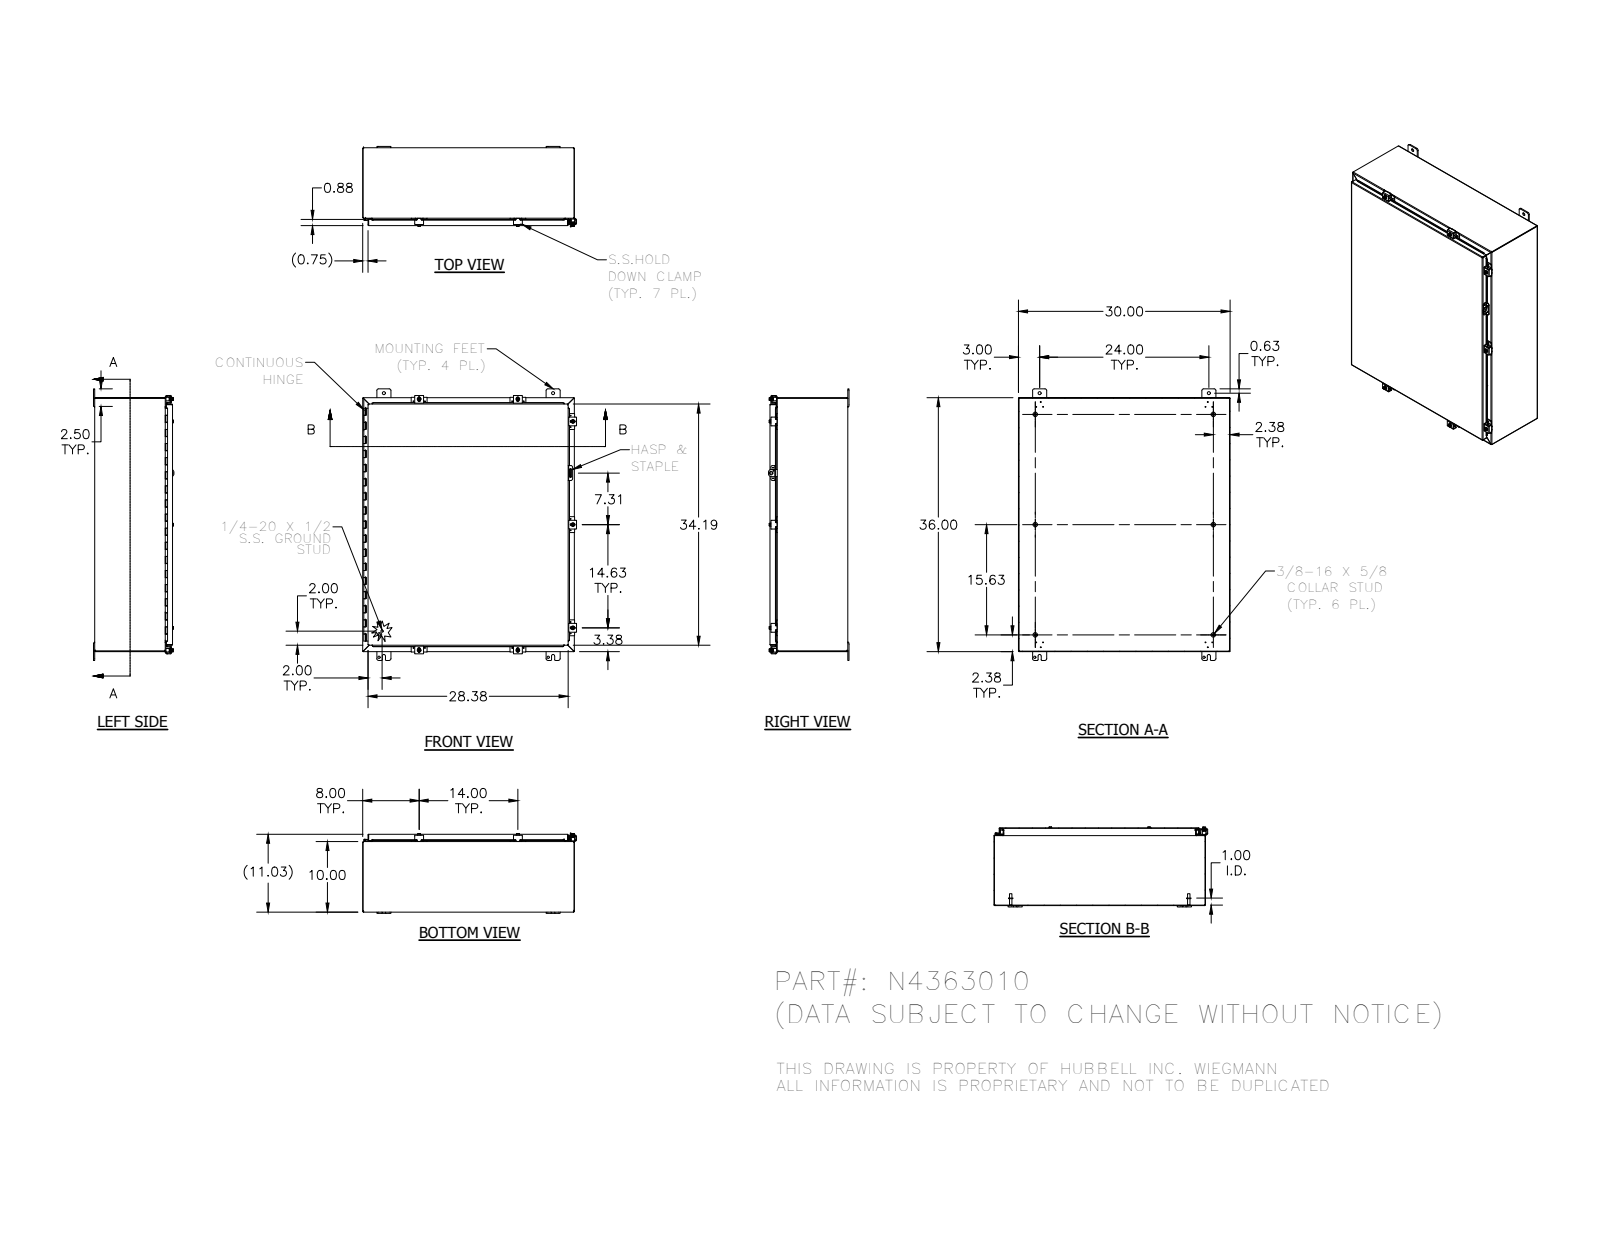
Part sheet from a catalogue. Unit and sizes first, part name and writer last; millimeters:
Units: millimetres
Overall size (bounding box): 977.9 × 769.9 × 289.8
Round holes (diameter × count): ⌀2.8 ×17, ⌀3 ×12, ⌀5.4 ×7, ⌀7.1 ×7, ⌀7.6 ×7, ⌀8 ×4, ⌀11.1 ×4, ⌀3.2 ×1, ⌀4 ×1, ⌀12.7 ×1
Round bosses / shafts (diameter × count): ⌀6.4 ×9, ⌀13.2 ×7, ⌀12.7 ×7, ⌀8.9 ×7, ⌀15.9 ×6, ⌀8.4 ×6, ⌀2.9 ×2, ⌀8.6 ×1
Partial cylindrical surfaces — rounded edges, fillets, slot ends (radius × count): R0.8 ×83, R1.6 ×41, R3.2 ×37, R6.4 ×33, R0.8 ×23, R2.7 ×23, R1.6 ×14, R3.6 ×14
Main face-to-face distances: 1.9, 278.4, 276.5, 280.2, 760.1, 912.5, 758.2, 762, 252.1, 26.2
Hole centre spacings: 609.6, 22.3, 19.3, 23.9, 24.6, 50.7, 593.5, 618.1
Volume: 4 977 000 mm³ · Surface area: 5 160 000 mm²
Bodies: 54 solids, 2404 faces (930 planar, 1087 cylindrical, 387 other)
Part name (STEP PRODUCT): 32911_1; HFW30825-3_1; 30824-1_1; 34x28_1 (+8 more)
STEP written by: SolidWorks 2014 (AUTOMOTIVE_DESIGN)
